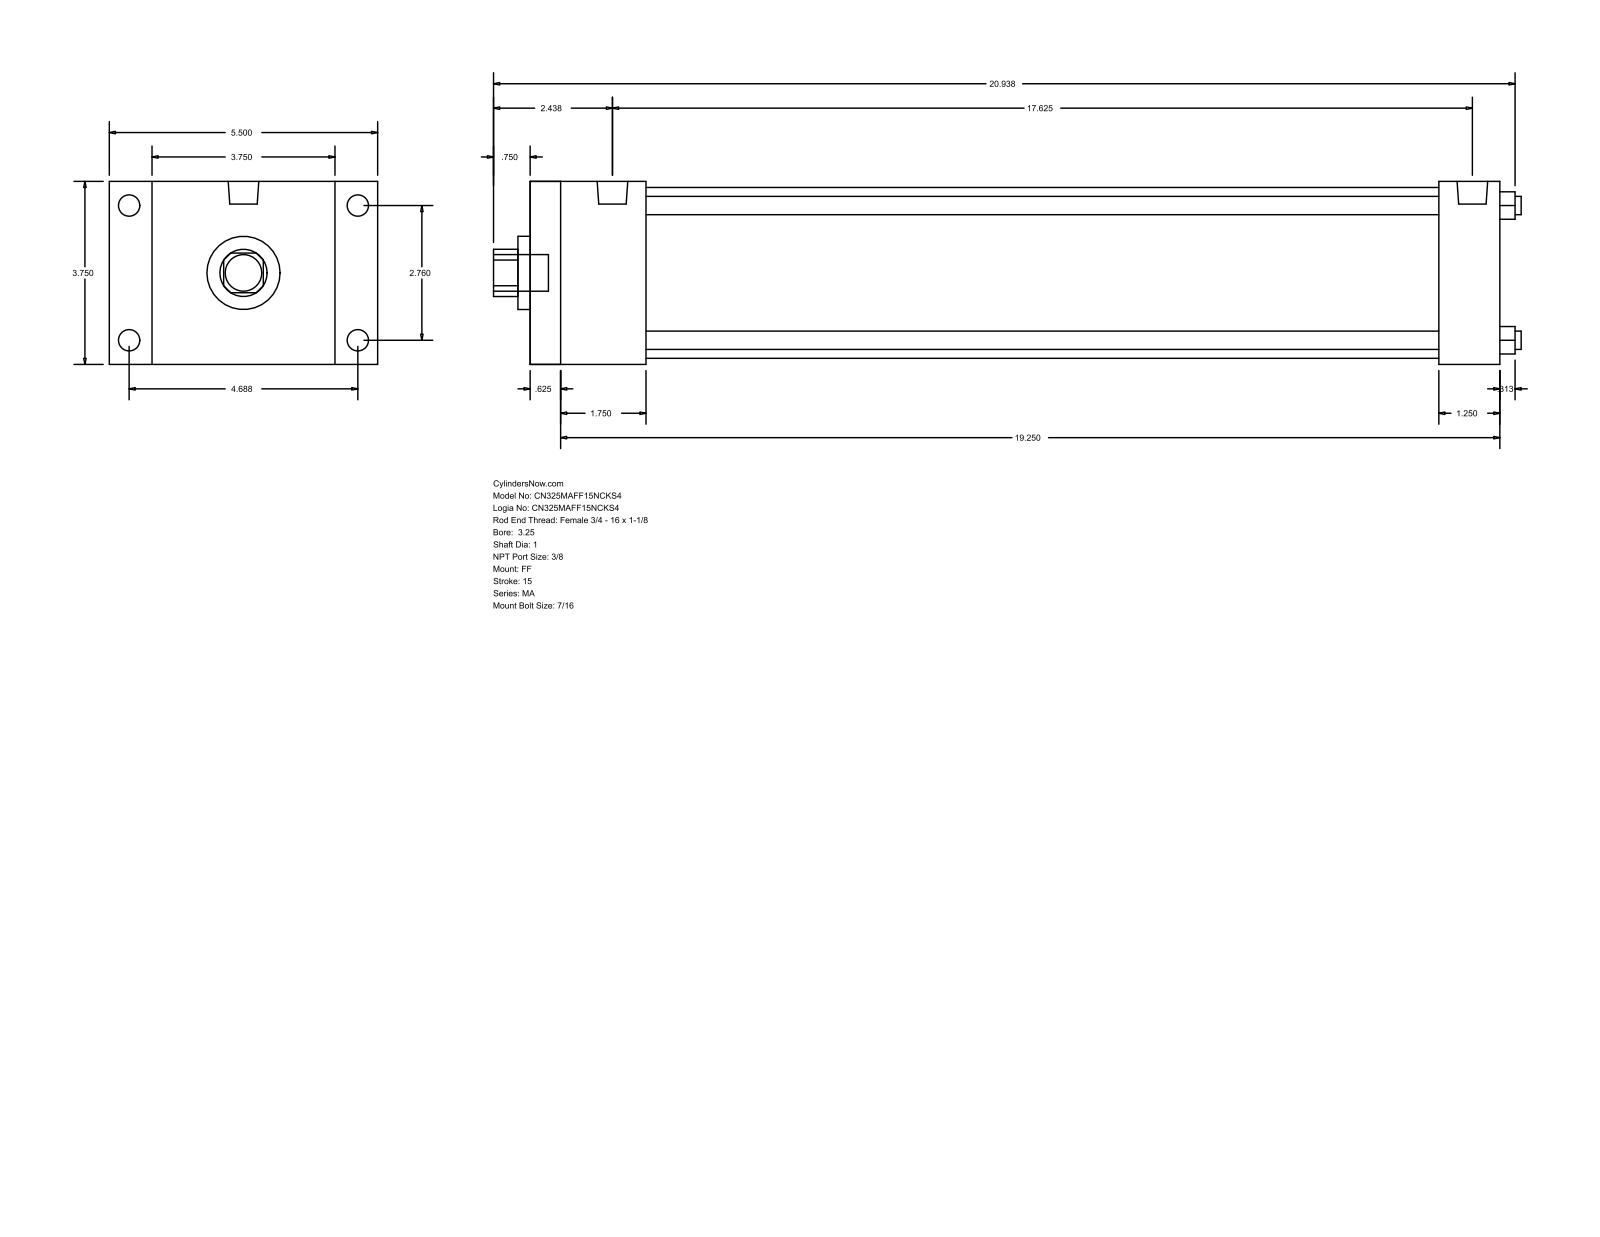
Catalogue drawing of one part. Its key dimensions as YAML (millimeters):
part_name: "MA_FF__0325_1"
step_written_by: "GSSL Pune (CONFIG_CONTROL_DESIGN)"
units: millimeters
bodies: {solids: 0, faces: 92, planar: 64, cylindrical: 28, other: 0}
overall_size: [534.99, 139.7, 95.25]
round_holes:
  - {diameter: 9.53, count: 4}
  - {diameter: 25.4, count: 1}
  - {diameter: 38.1, count: 1}
  - {diameter: 88.9, count: 1}
round_bosses_or_shafts:
  - {diameter: 11.11, count: 8}
  - {diameter: 15.93, count: 2}
  - {diameter: 19.05, count: 1}
partial_cylinders:
  - {radius: 12.29, count: 1}
face_to_face_distances: [95.24, 504.83, 15.87, 488.96, 22.23, 117.47, 60.33, 473.07, 44.46, 457.2]
hole_center_spacings: [49.57, 70.1, 99.14]
